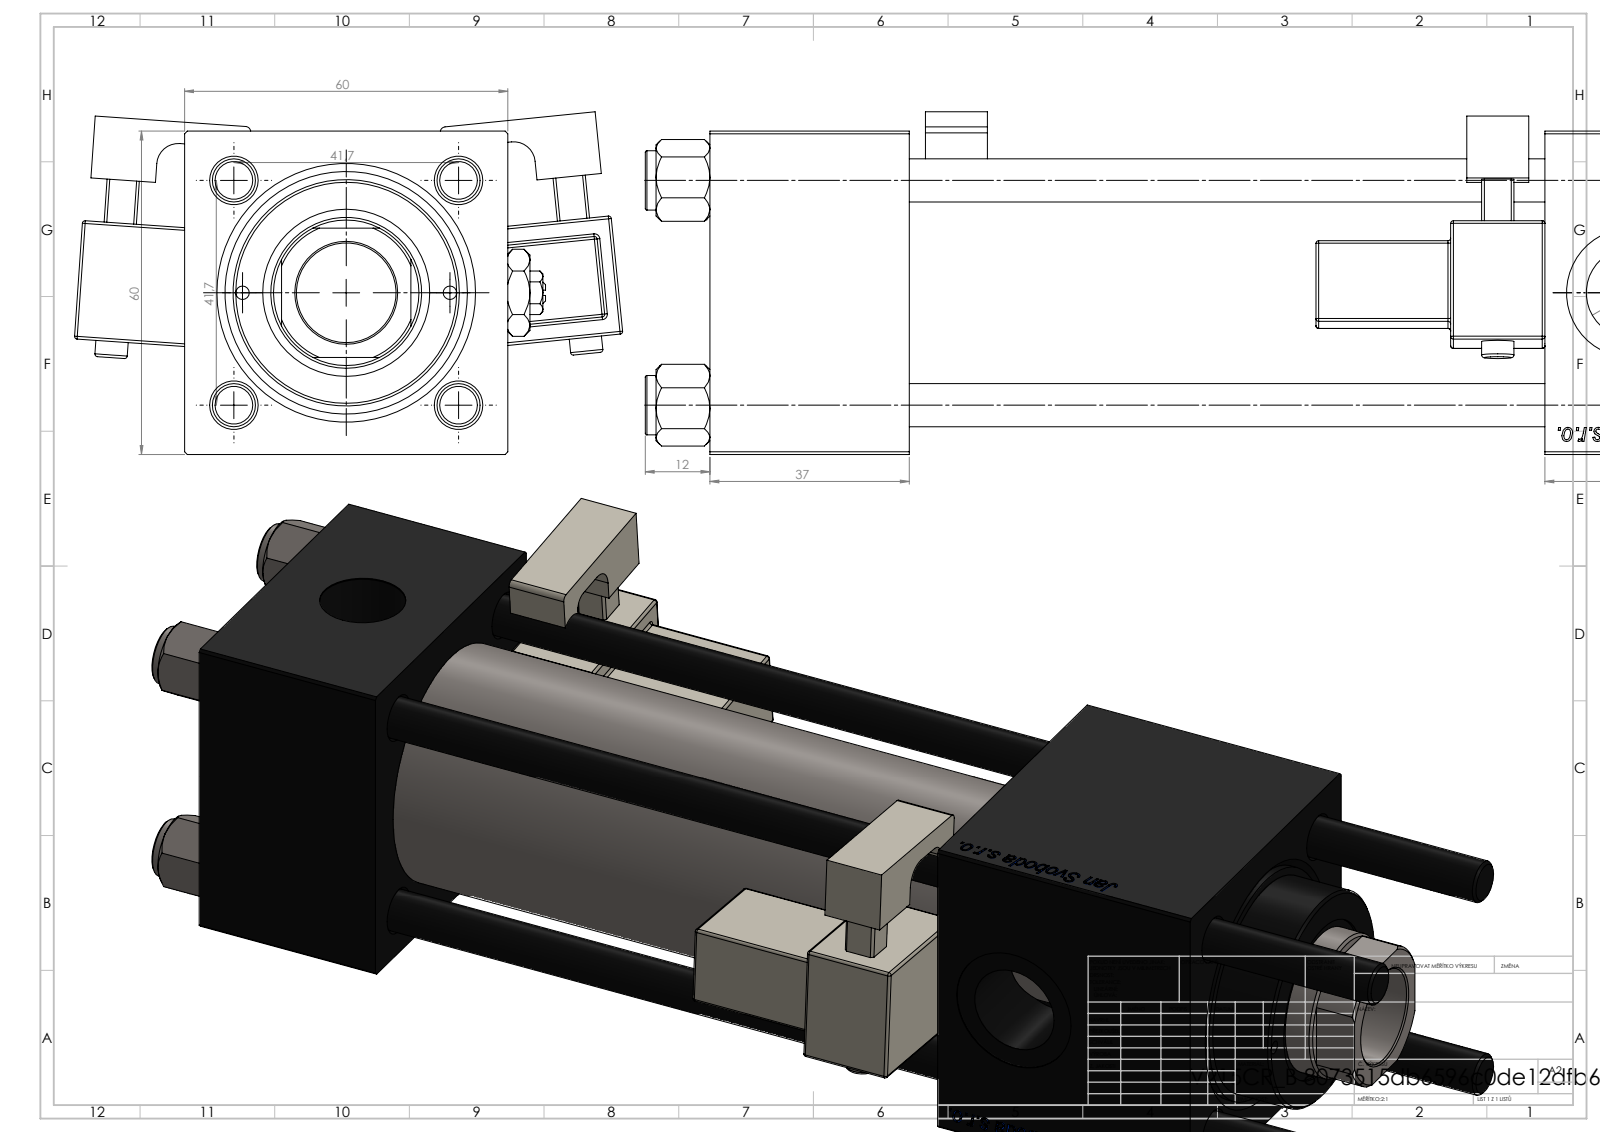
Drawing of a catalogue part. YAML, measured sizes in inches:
part_name: "V215CR_MSU; V215CR_VCP_B; V215CR_B-1; V215CR_B_TYCINKA (+3 more)"
step_written_by: "SolidWorks 2019 (CONFIG_CONTROL_DESIGN)"
units: inches
bodies: {solids: 10, faces: 1363, planar: 516, cylindrical: 143, other: 704}
overall_size: [10.039, 4.005, 2.503]
volume: 30.24
surface_area: 229.5
round_holes:
  - {diameter: 0.315, count: 4}
  - {diameter: 0.098, count: 2}
  - {diameter: 0.276, count: 2}
  - {diameter: 0.656, count: 2}
  - {diameter: 0.63, count: 1}
  - {diameter: 0.728, count: 1}
  - {diameter: 0.945, count: 1}
  - {diameter: 1.102, count: 1}
  - {diameter: 1.22, count: 1}
  - {diameter: 1.575, count: 1}
  - {diameter: 1.772, count: 1}
round_bosses_or_shafts:
  - {diameter: 0.433, count: 4}
  - {diameter: 0.236, count: 2}
  - {diameter: 1.811, count: 1}
  - {diameter: 1.654, count: 1}
partial_cylinders:
  - {radius: 0.02, count: 48}
  - {radius: 0.039, count: 2}
  - {radius: 0.098, count: 2}
  - {radius: 0.157, count: 2}
  - {radius: 0.531, count: 1}
face_to_face_distances: [2.362, 1.457, 6.102, 4.646, 7.059, 5.602, 0.957, 2.087, 8.189, 6.732]
hole_center_spacings: [0.823, 1.161, 1.642, 1.78, 0.758, 2.322, 1.516]
